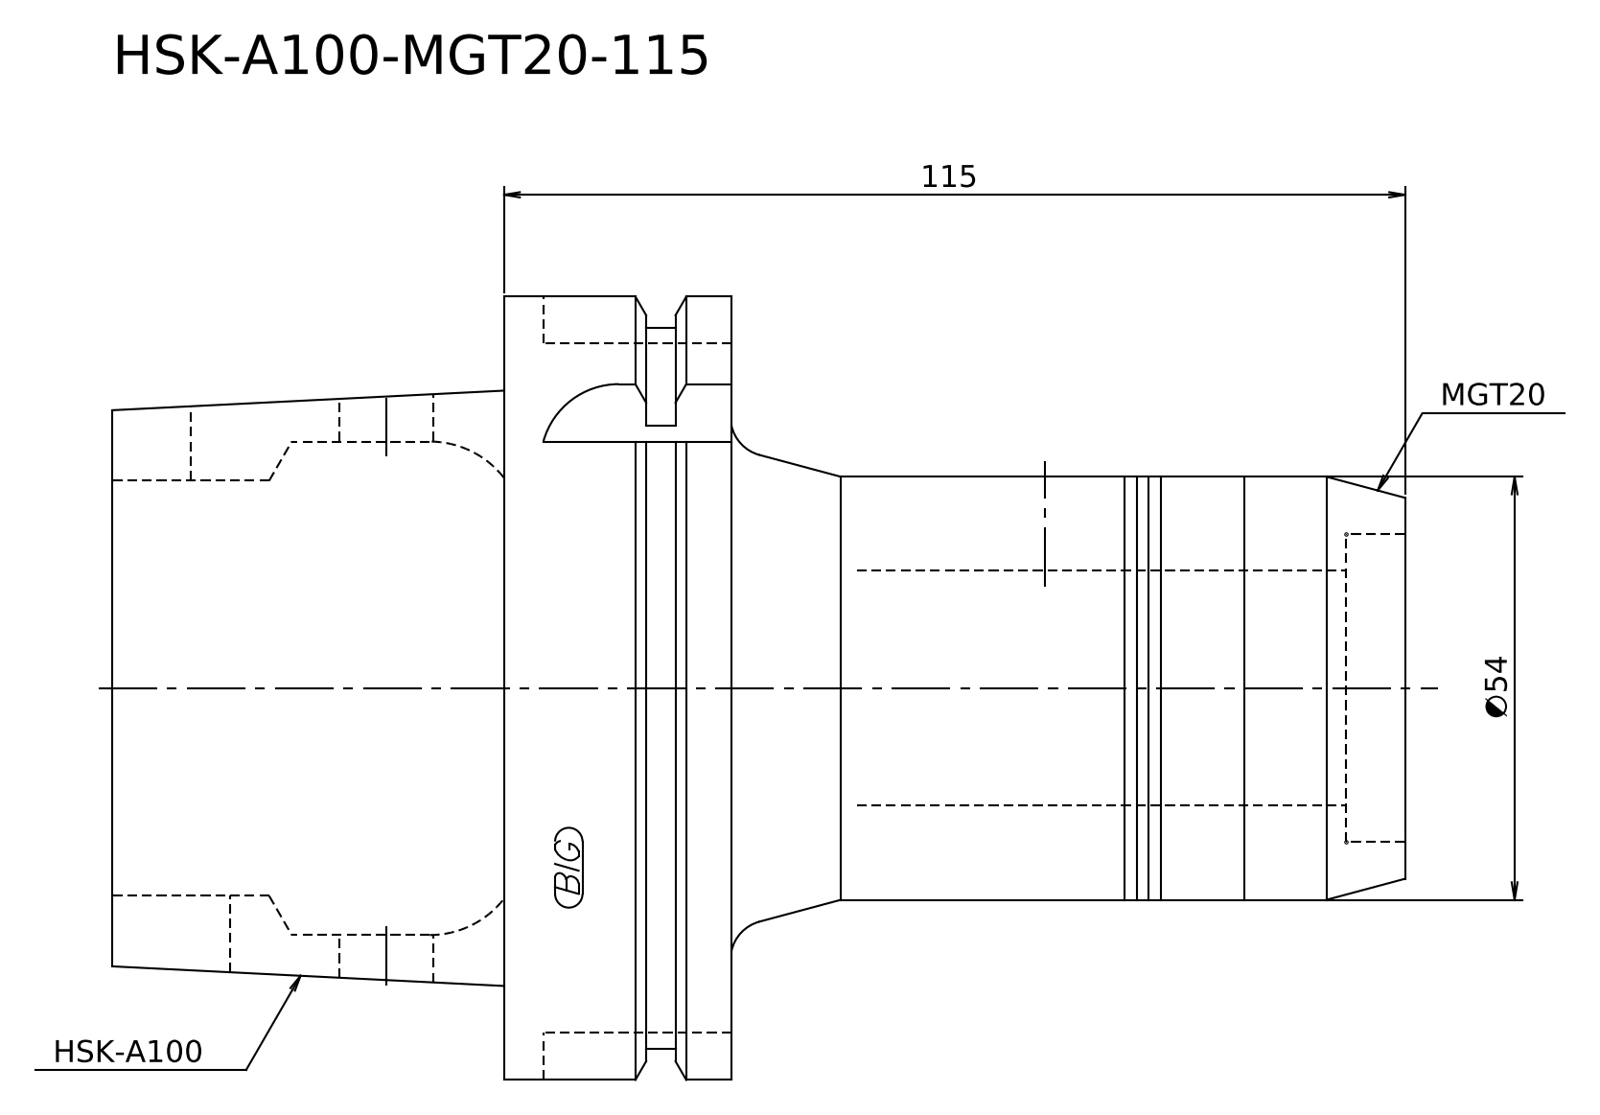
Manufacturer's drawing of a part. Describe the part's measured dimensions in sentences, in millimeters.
Its 3-D file was written by "Kubotek KeyCreator V8.5.1 (14335) (CONFIG_CONTROL_DESIGN)". It is 1 solid with 16 faces: 6 planar, 4 cylindrical and 6 other. Overall it measures 165 by 100 by 100 millimeters. Its volume is 635 299 cubic millimeters and its surface area 50 901 square millimeters. Round bosses or shafts: 1 of diameter 100, 1 of diameter 92, 1 of diameter 54. The main face-to-face distances are 79, 29, 50, 86, 115, 165, 96.88, 10.88, 18.12, 68.12.
